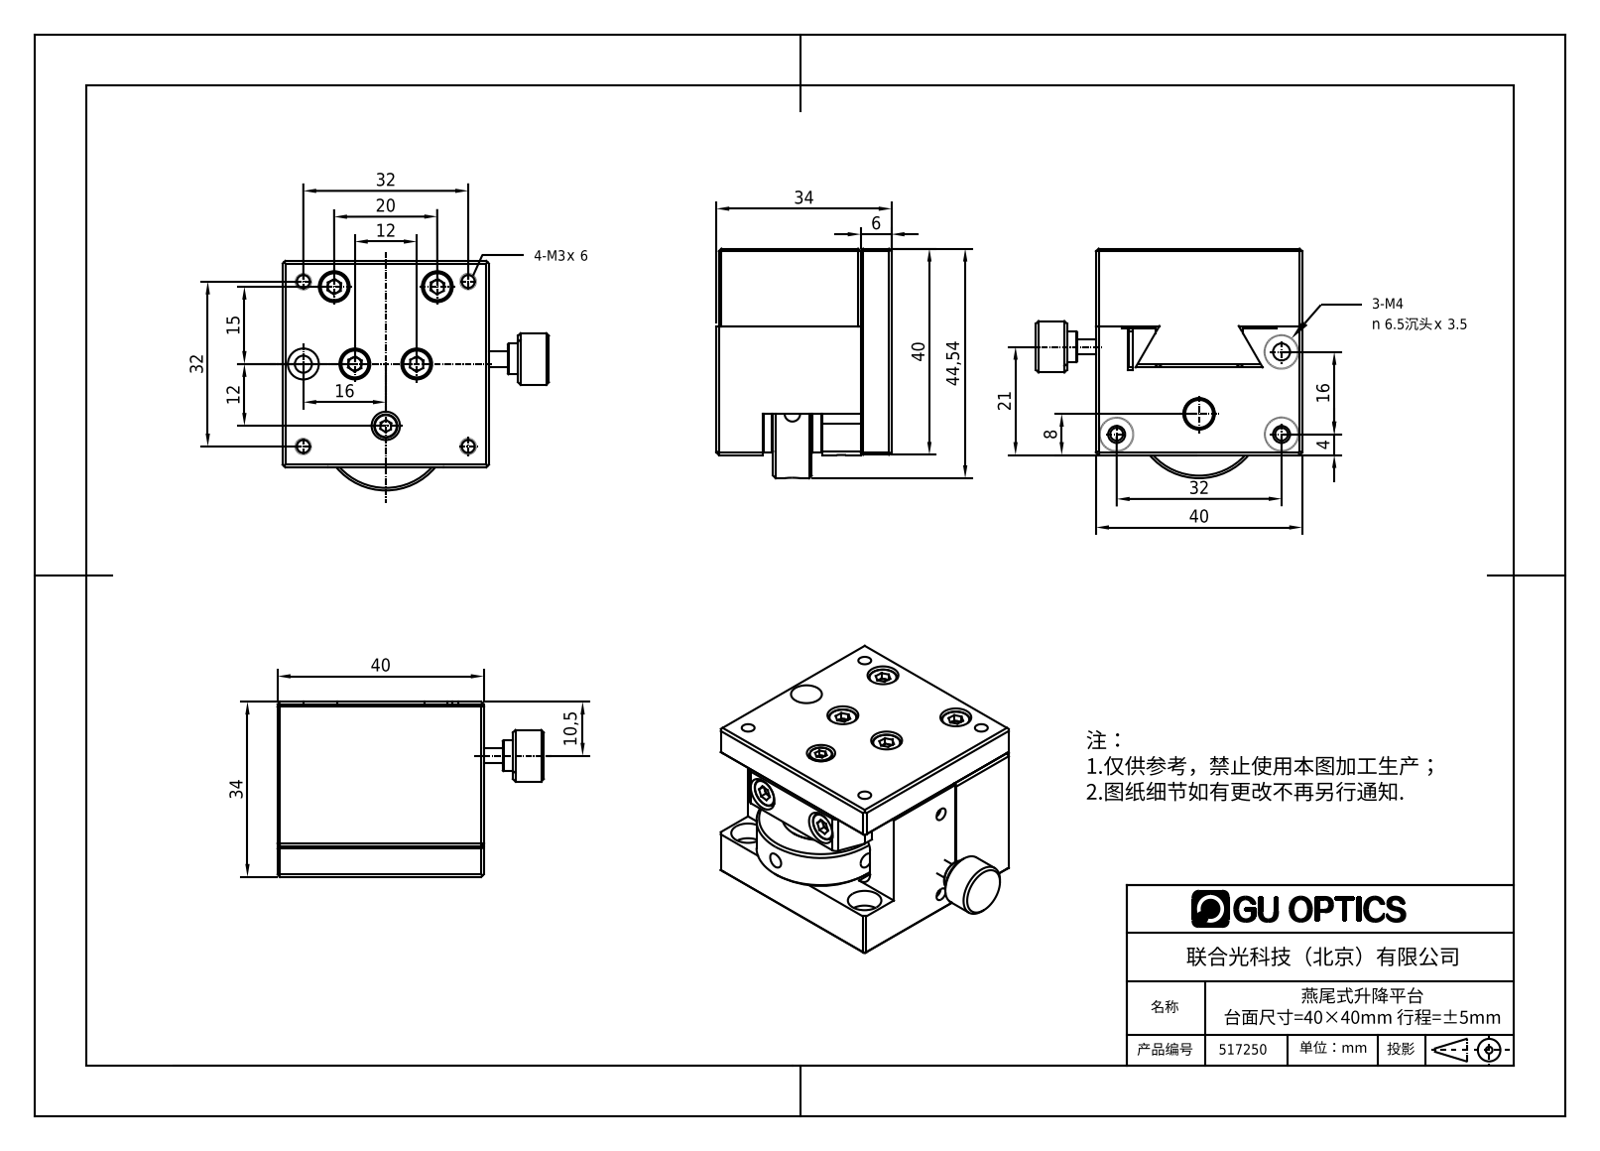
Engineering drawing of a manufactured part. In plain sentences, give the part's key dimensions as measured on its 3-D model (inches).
The part is named "517250". Its 3-D file was written by "SolidWorks 2020 (CONFIG_CONTROL_DESIGN)". It is 0 solids with 293 faces: 175 planar, 71 cylindrical and 47 other. Overall it measures 2.033 by 1.754 by 1.339 inches. Round holes: 6 of diameter 0.098, 5 of diameter 0.236, 4 of diameter 0.256, 3 of diameter 0.13, 1 of diameter 0.217, 1 of diameter 0.24, 1 of diameter 0.984. Round bosses or shafts: 3 of diameter 0.118, 2 of diameter 0.217, 1 of diameter 0.591, 1 of diameter 0.394, 1 of diameter 0.236, 1 of diameter 0.177. Partial cylindrical surfaces (rounded edges, fillets, slot ends): 4 of radius 0.118, 2 of radius 0.039, 1 of radius 0.02. The main face-to-face distances are 0.236, 1.575, 0.02, 0.374, 0.295, 0.669, 0.984, 1.102, 0.591, 1.319. The hole center spacings are 1.26, 0.63, 0.649, 0.743, 1.071, 0.787, 1.409, 0.239.
